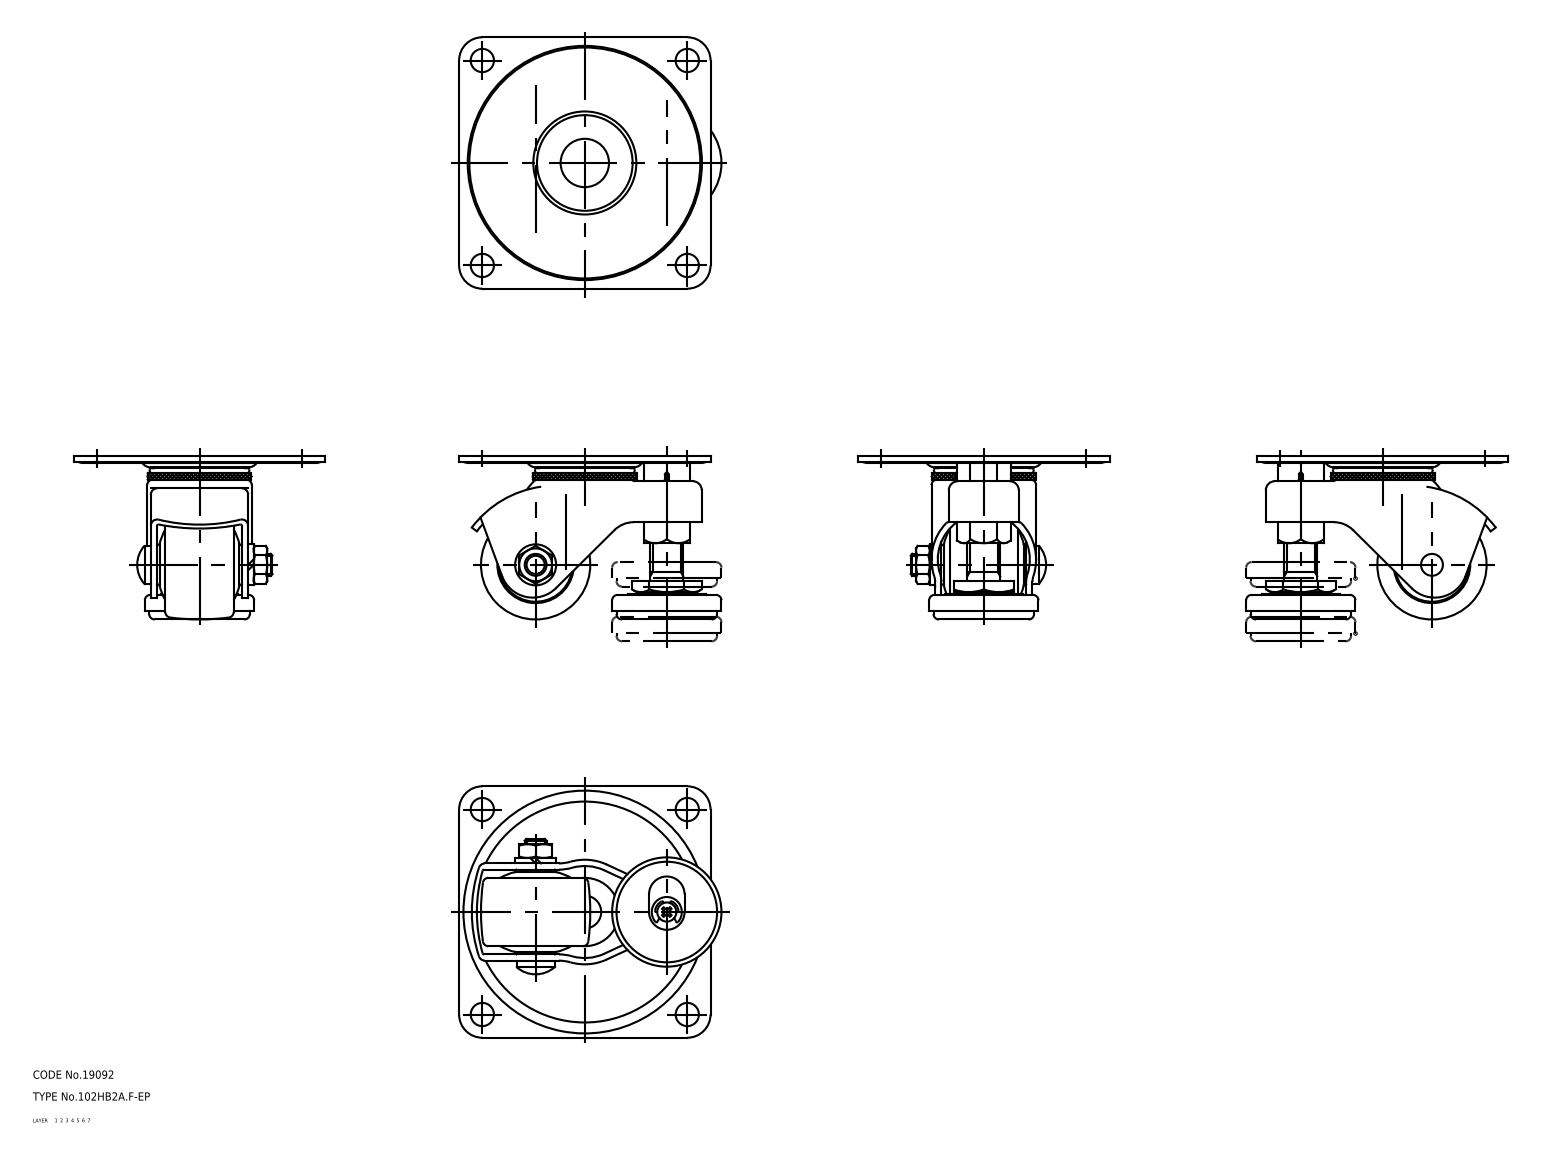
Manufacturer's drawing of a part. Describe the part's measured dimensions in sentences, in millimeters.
The part is named "wheel; mounting plate; main shaft; foot (+2 more)". Its 3-D file was written by "CADfix (AUTOMOTIVE_DESIGN)". It is 6 solids with 357 faces: 0 planar, 0 cylindrical and 357 other. Overall it measures 96 by 92 by 60 millimeters. Its volume is 97 392 cubic millimeters and its surface area 48 714 square millimeters.
